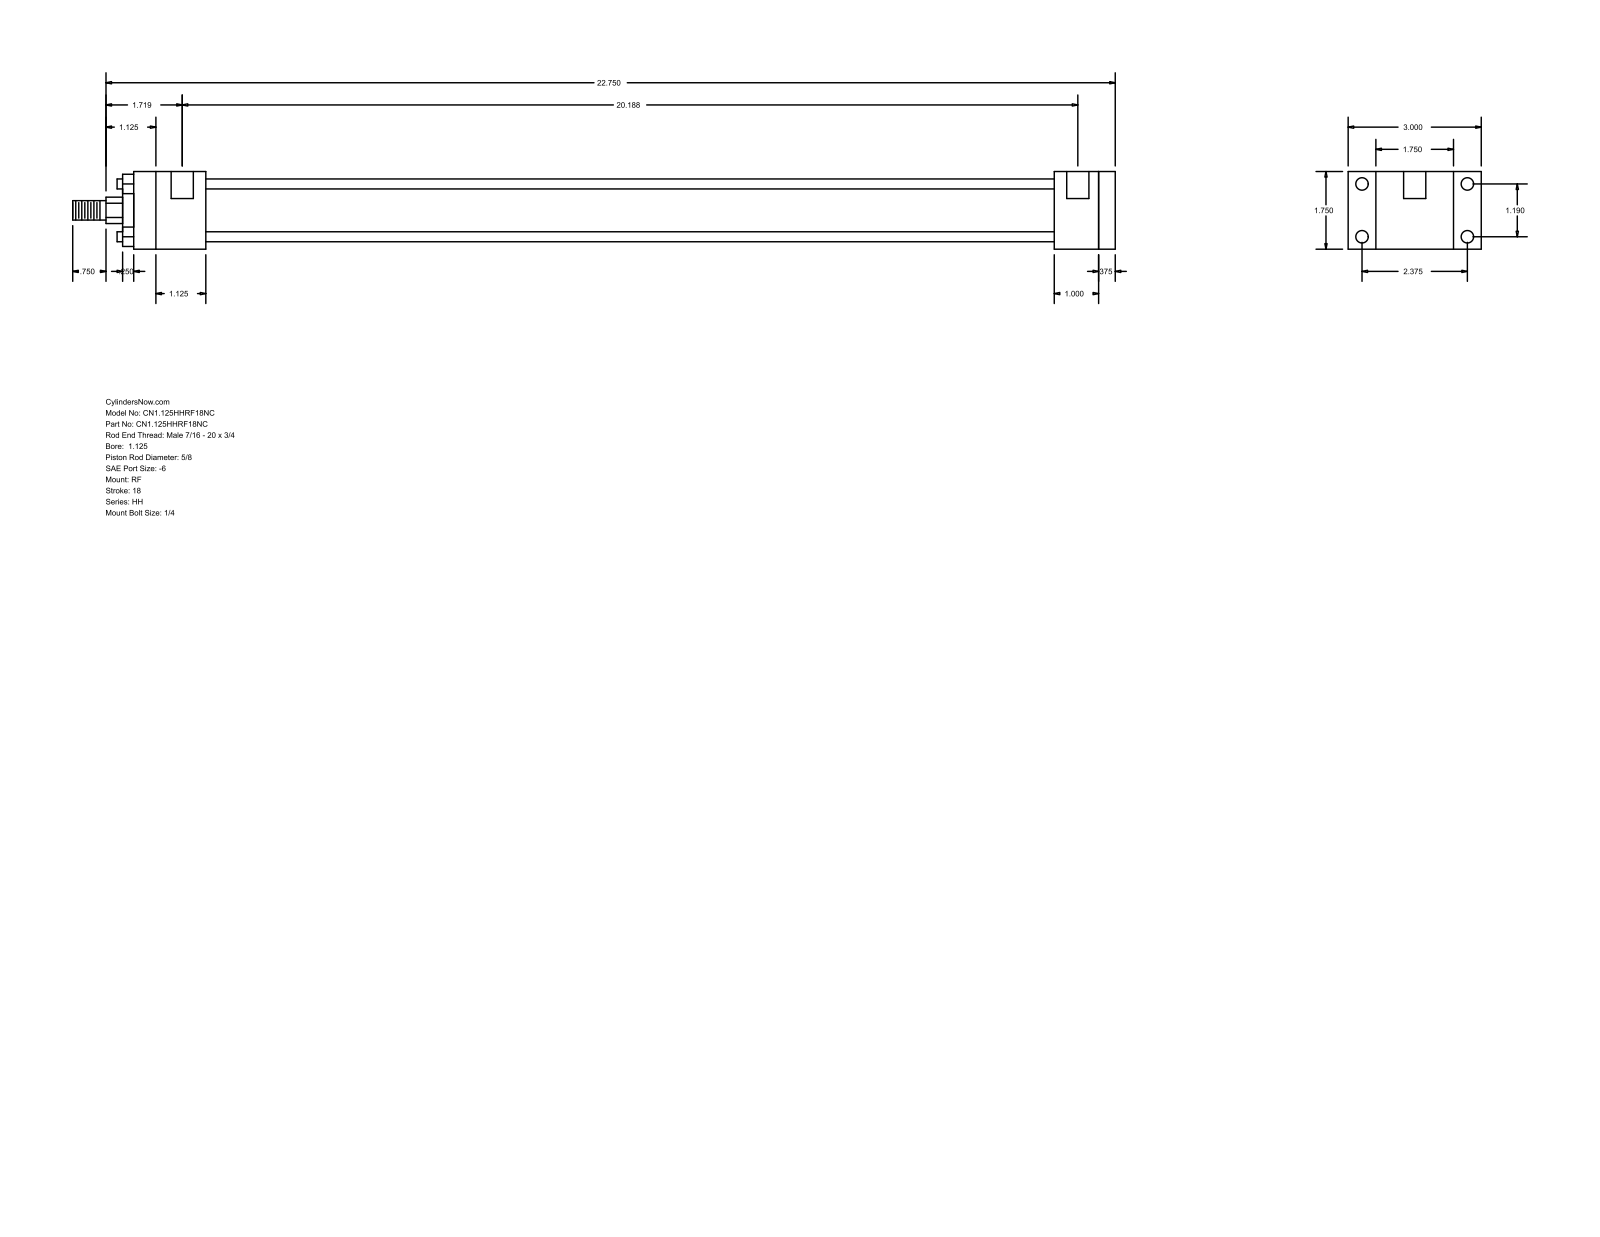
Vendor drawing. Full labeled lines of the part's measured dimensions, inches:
Part name (STEP PRODUCT): HH_RF__0112_0.625
STEP written by: GSSL Pune (CONFIG_CONTROL_DESIGN)
Units: inches
Bodies: 0 solids, 92 faces (64 planar, 28 cylindrical, 0 other)
Overall size (bounding box): 23.5 × 3 × 1.75
Round holes (diameter × count): ⌀0.219 ×4, ⌀0.281 ×4, ⌀0.5 ×2
Round bosses / shafts (diameter × count): ⌀0.225 ×4, ⌀1.375 ×1, ⌀1.125 ×1, ⌀0.625 ×1, ⌀0.437 ×1
Partial cylindrical surfaces — rounded edges, fillets, slot ends (radius × count): R0.297 ×1
Main face-to-face distances: 1.75, 0.375, 1.375, 22.125, 0.625, 20.125, 20.5, 19.125, 1, 1.625
Hole centre spacings: 1.19, 2.375, 2.656, 20.063, 0.125, 20.187
